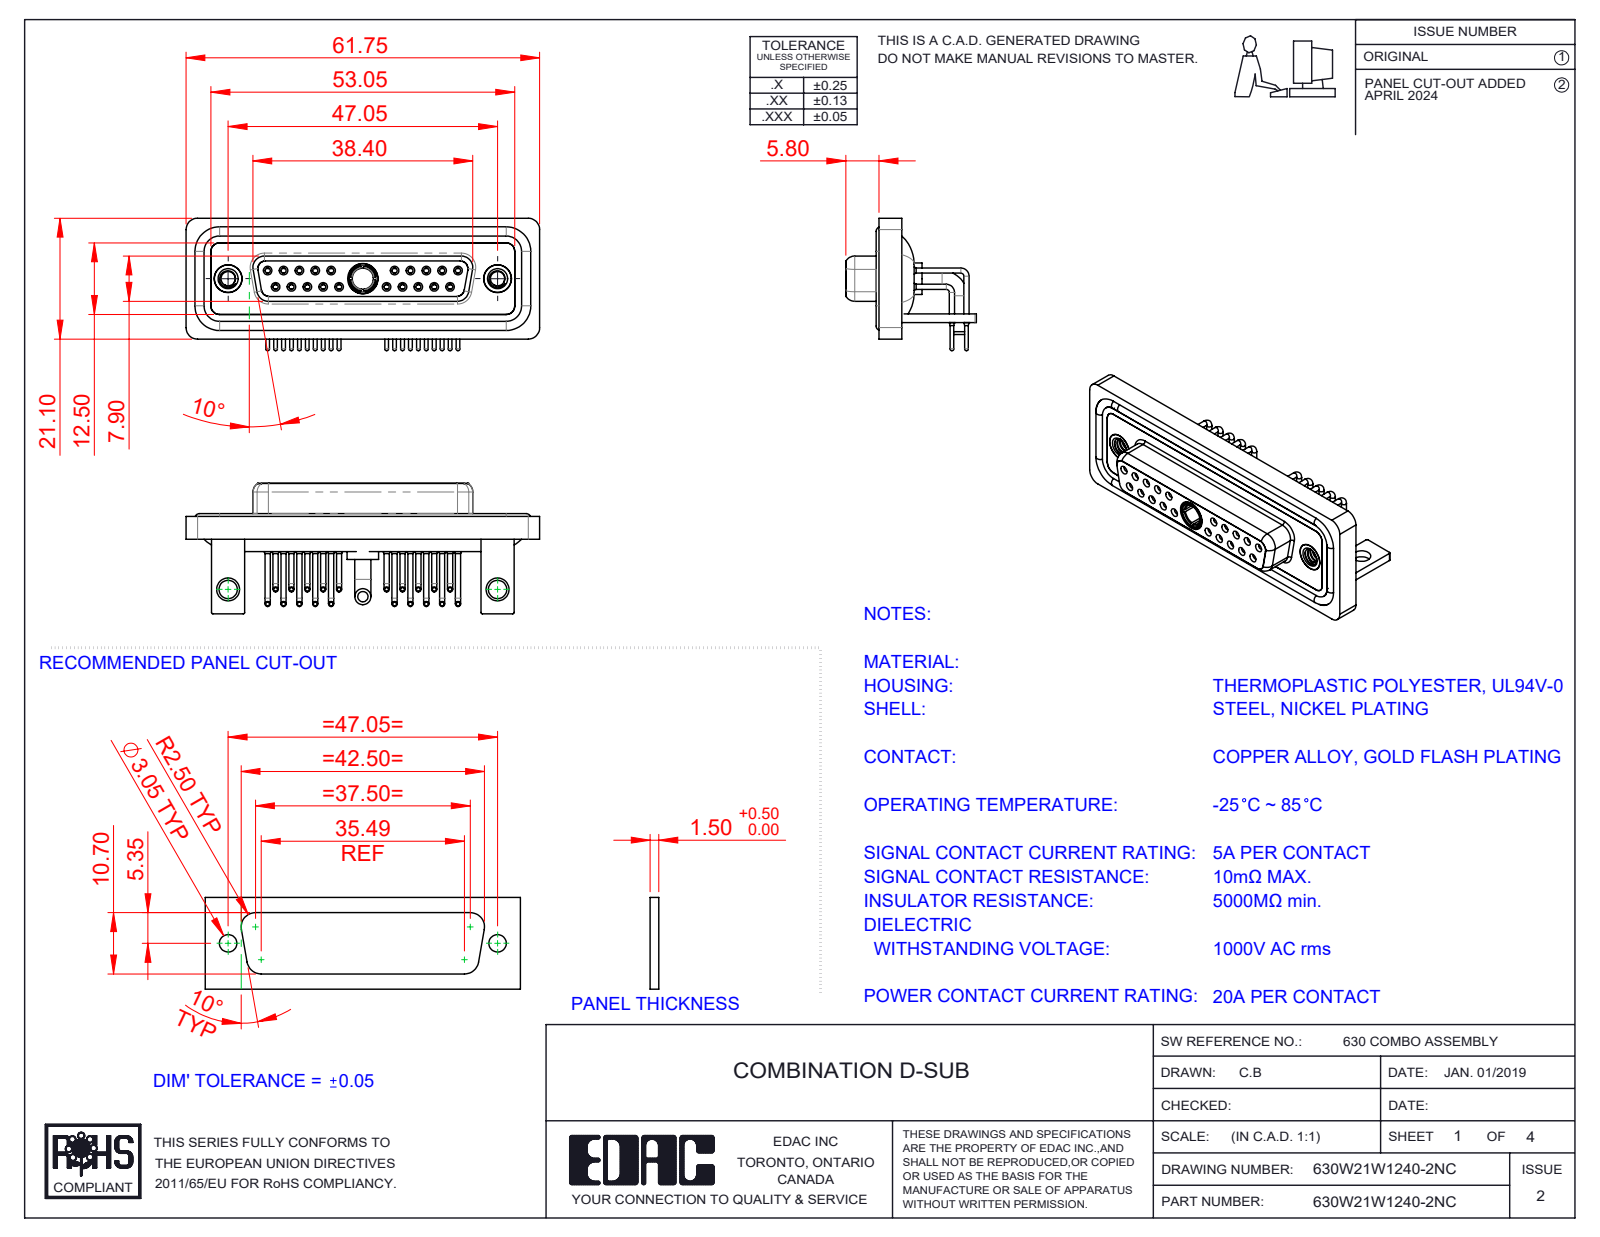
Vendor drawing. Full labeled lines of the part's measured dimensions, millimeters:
Part name (STEP PRODUCT): 630Combo Shell Front_25 Contacts; Power Socket_20A RA; 630Combo Contact Row 2_50 Contacts; 630Combo Waterproof Housing_25 Contacts (+6 more)
STEP written by: SolidWorks 2023 (CONFIG_CONTROL_DESIGN)
Units: millimetres
Bodies: 31 solids, 1566 faces (454 planar, 695 cylindrical, 417 other)
Overall size (bounding box): 61.75 × 23.12 × 22.8
Volume: 8 865 mm³ · Surface area: 15 518 mm²
Round holes (diameter × count): ⌀0.9 ×20, ⌀1.1 ×20, ⌀1.5 ×20, ⌀2 ×20, ⌀1.6 ×10, ⌀1.7 ×10, ⌀4.85 ×3, ⌀2.5 ×2, ⌀3.2 ×2, ⌀4 ×2, ⌀4.05 ×2, ⌀5 ×2
Round bosses / shafts (diameter × count): ⌀0.9 ×20, ⌀0.65 ×20, ⌀1.6 ×14, ⌀4.95 ×2, ⌀4.8 ×2, ⌀2.8 ×2, ⌀5.5 ×1, ⌀5.2 ×1
Partial cylindrical surfaces — rounded edges, fillets, slot ends (radius × count): R2 ×19, R1.5 ×18, R0.25 ×16, R1.35 ×8, R1.6 ×8, R0.5 ×5, R0.6 ×4, R0.65 ×4
Main face-to-face distances: 0.4, 1.8, 2.9, 3.7, 1.5, 4.1, 1.1, 1.4, 1.6, 2.5
Hole centre spacings: 3.16, 2.77, 5.54, 8.31, 5.04, 19.39, 20.97, 22.16
